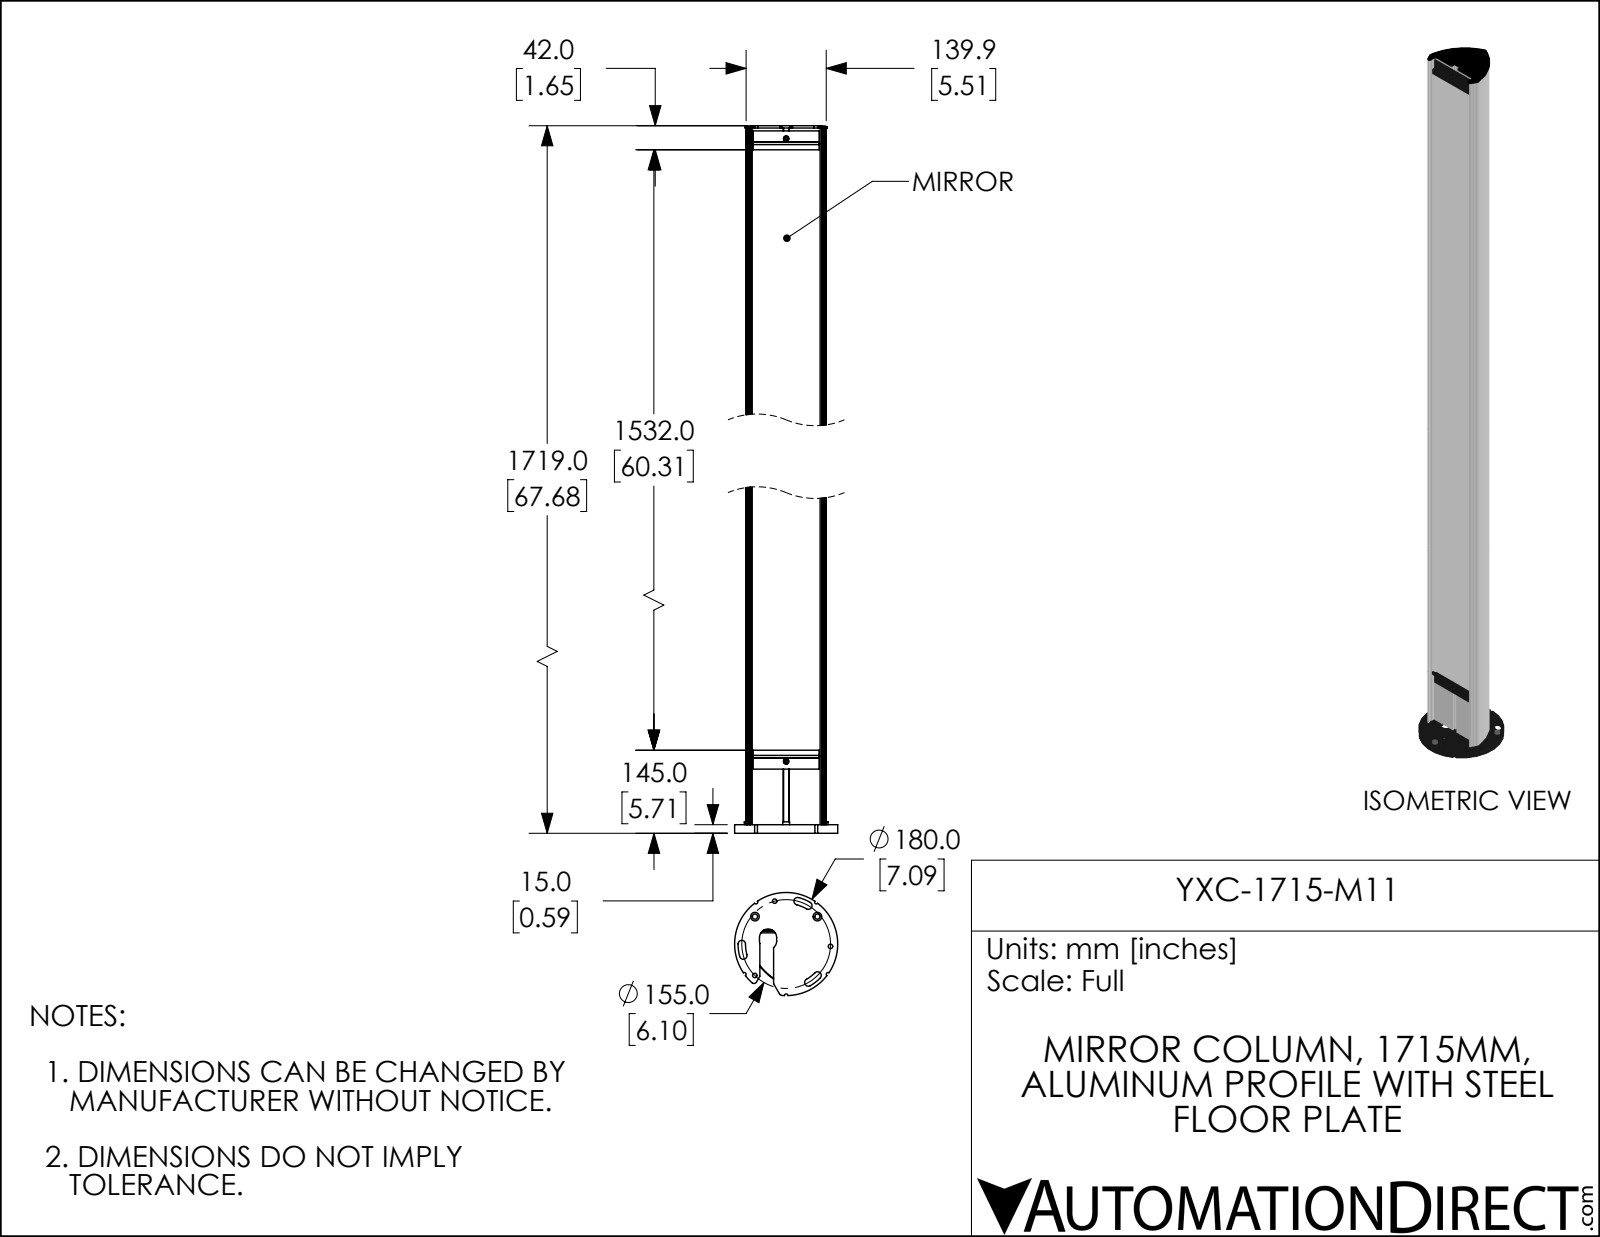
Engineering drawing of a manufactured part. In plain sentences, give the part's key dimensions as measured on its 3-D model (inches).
The part is named "YXC-1715-M11". Its 3-D file was written by "SolidWorks 2019 (AUTOMOTIVE_DESIGN)". It is 1 solid with 290 faces: 187 planar, 88 cylindrical and 15 other. Overall it measures 67.677 by 7.087 by 7.085 inches. Its volume is 996.3 cubic inches and its surface area 1 404 square inches. Round holes: 3 of diameter 0.307, 3 of diameter 0.591, 2 of diameter 0.354, 1 of diameter 0.173. Round bosses or shafts: 3 of diameter 0.472, 2 of diameter 0.374, 2 of diameter 0.335, 1 of diameter 7.087. Partial cylindrical surfaces (rounded edges, fillets, slot ends): 9 of radius 0.118, 6 of radius 0.256, 5 of radius 0.236, 4 of radius 0.039, 4 of radius 0.052, 4 of radius 4.685, 3 of radius 0.197, 2 of radius 0.052. The main face-to-face distances are 0.118, 0.157, 0.335, 0.492, 0.591, 0.453, 0.098, 0.382, 0.224, 0.11. The hole center spacings are 2.146, 1.255, 1.257, 1.722, 2.235, 3.121, 3.717, 3.719.
